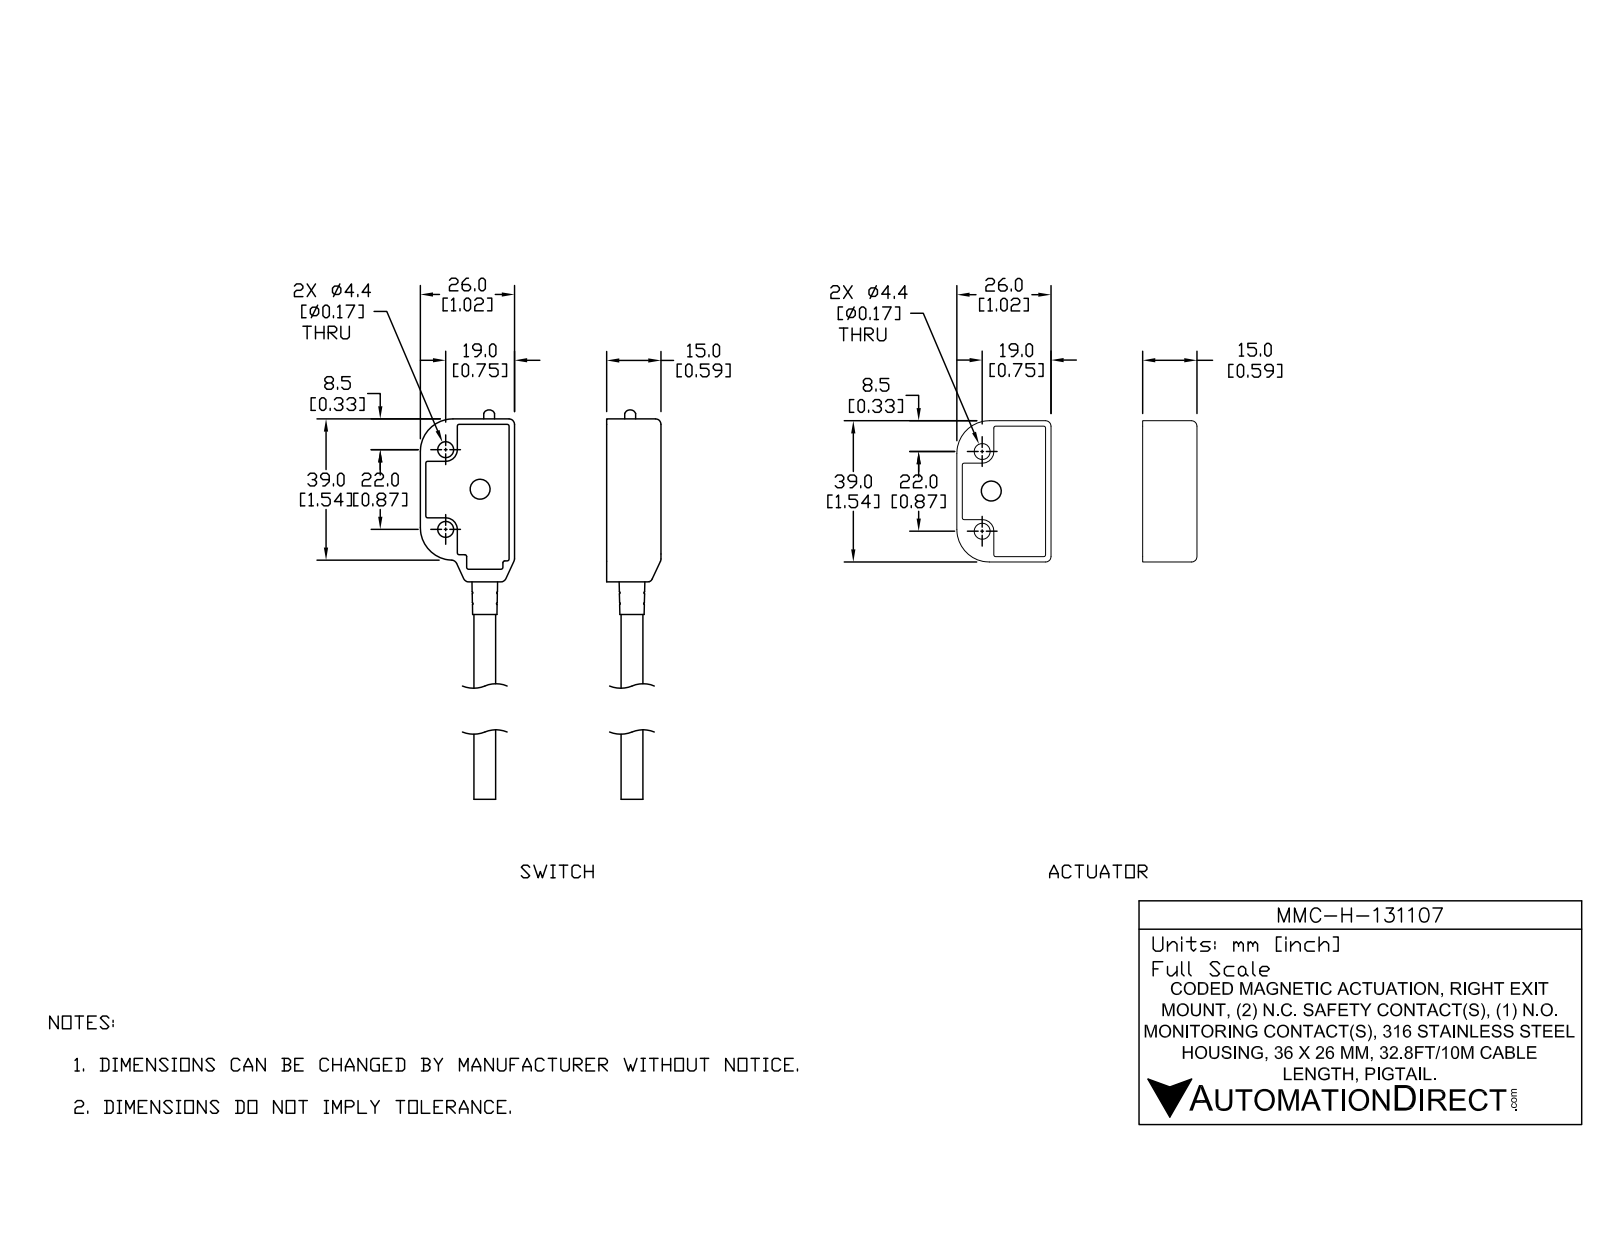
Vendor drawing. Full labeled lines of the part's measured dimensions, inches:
Part name (STEP PRODUCT): MMC-H-131107_2; MMC-H-131107_1; MMC-H-131107
STEP written by: SolidWorks 2017 (AUTOMOTIVE_DESIGN)
Units: inches
Bodies: 9 solids, 599 faces (178 planar, 232 cylindrical, 189 other)
Overall size (bounding box): 7.902 × 2.087 × 0.591
Volume: 1.233 in³ · Surface area: 31 in²
Round holes (diameter × count): ⌀0.173 ×4, ⌀0.197 ×2, ⌀0.118 ×1, ⌀0.232 ×1, ⌀0.283 ×1
Round bosses / shafts (diameter × count): ⌀0.079 ×2, ⌀0.031 ×2, ⌀0.339 ×1, ⌀0.299 ×1, ⌀0.28 ×1, ⌀0.236 ×1, ⌀0.157 ×1
Partial cylindrical surfaces — rounded edges, fillets, slot ends (radius × count): R0.02 ×82, R0.012 ×26, R0.059 ×15, R0.008 ×8, R0.157 ×6, R0.126 ×4, R0.13 ×4, R0.181 ×4
Main face-to-face distances: 0.059, 0.575, 0.516, 0.098, 0.461, 0.52, 0.055, 0.591, 0.531, 0.965
Hole centre spacings: 0.866, 1.535, 1.763, 0.076, 0.44, 0.448, 0.569, 0.575
